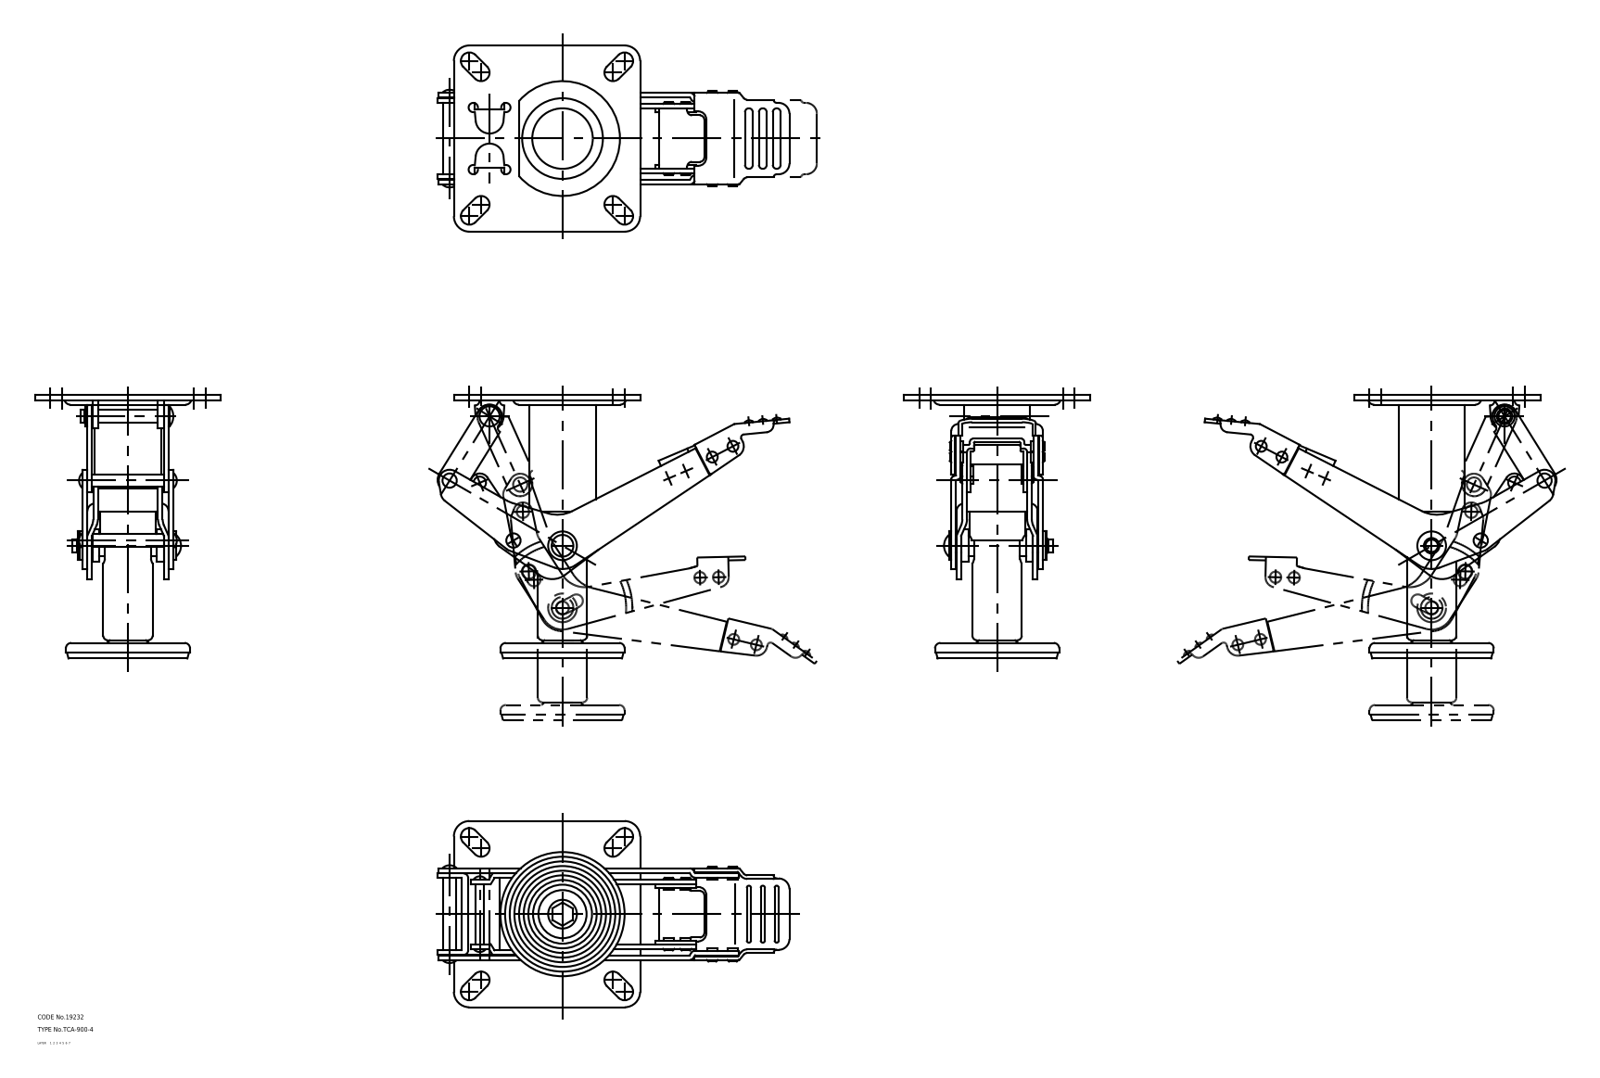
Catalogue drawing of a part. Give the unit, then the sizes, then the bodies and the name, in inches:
Units: inches
Overall size (bounding box): 8.924 × 6.693 × 4.724
Volume: 16.53 in³ · Surface area: 266.9 in²
Bodies: 6 solids, 543 faces (0 planar, 0 cylindrical, 543 other)
Part name (STEP PRODUCT): pedal_A; support rod_B; support rod_A; pedal_B (+3 more)
STEP written by: CADfix (AUTOMOTIVE_DESIGN)
